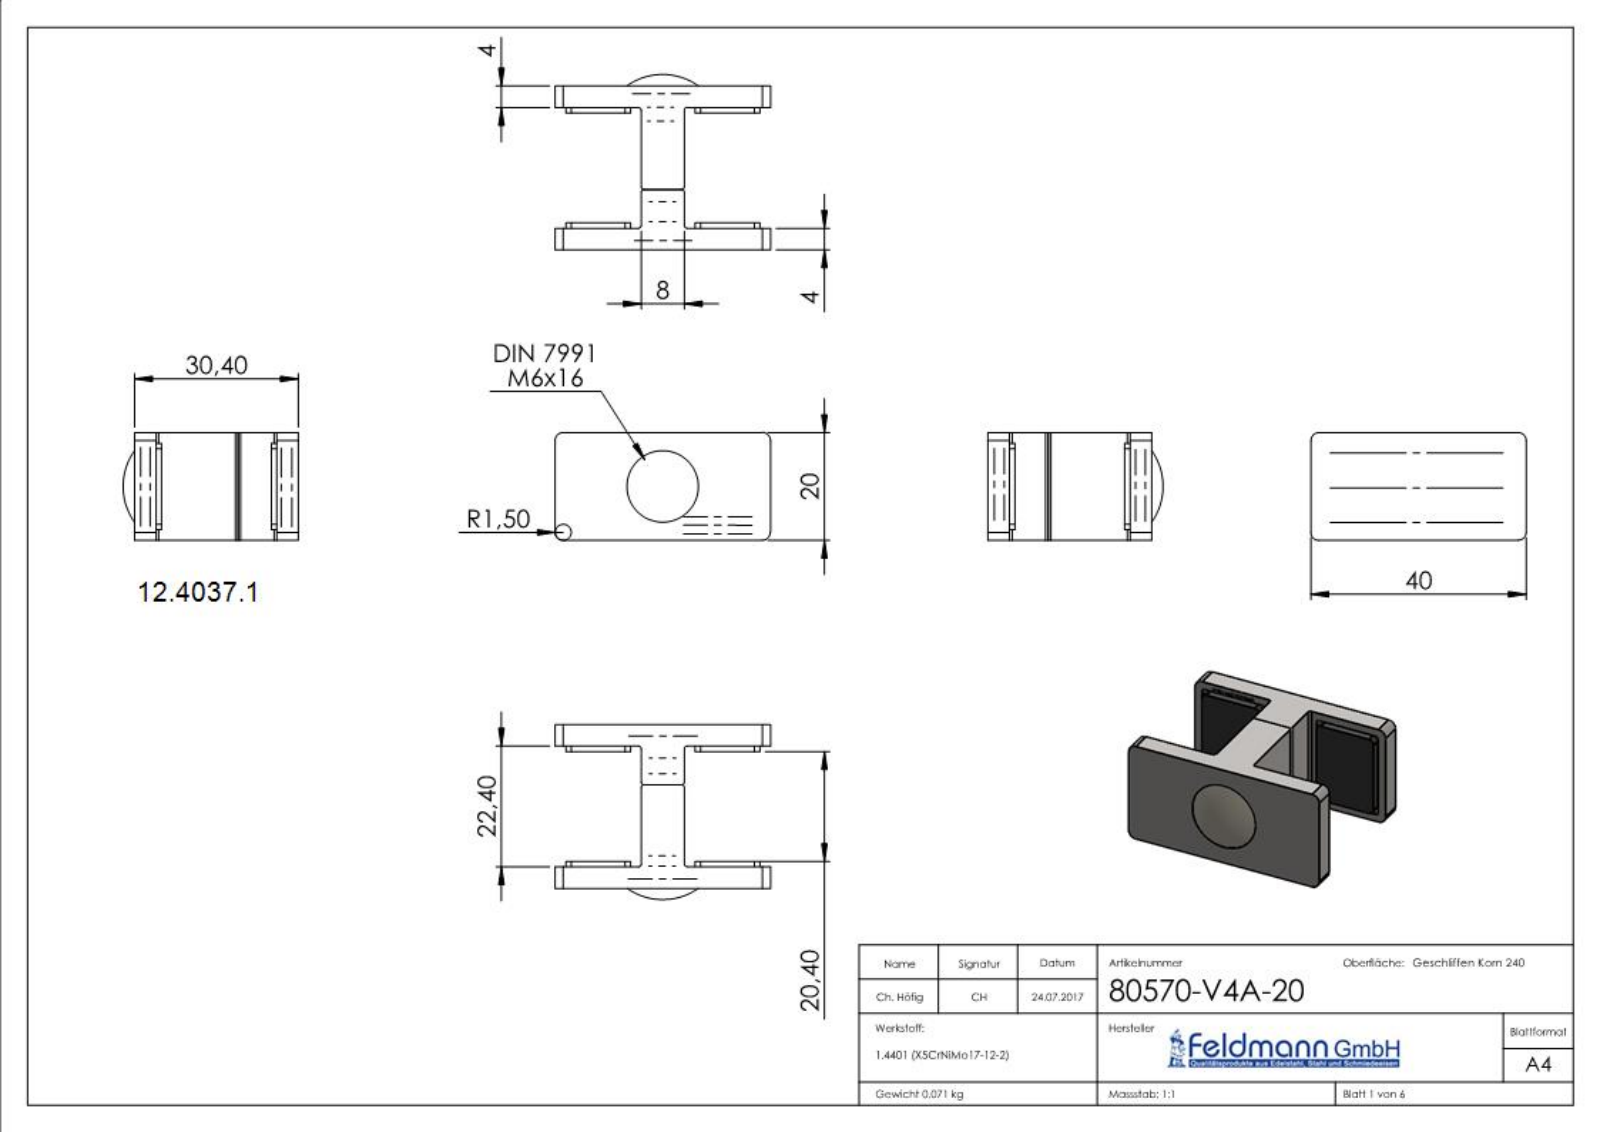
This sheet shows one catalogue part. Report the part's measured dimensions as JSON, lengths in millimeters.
{"part_name": "80570-XXX-XX Teil4_80570-XXX-XX Teil4; 80570-XXX-XX Teil4; 80570-V4A-20; 80570-XXX-XX Teil3_80570-240-XX Teil3 (+7 more)", "step_written_by": "SolidWorks 2018 (CONFIG_CONTROL_DESIGN)", "units": "millimeters", "bodies": {"solids": 8, "faces": 816, "planar": 380, "cylindrical": 203, "other": 233}, "overall_size": [40, 32.51, 20], "volume_mm3": 10149, "surface_area_mm2": 9084, "round_holes": [[2.7, 2], [1.8, 1], [5, 1], [6.5, 1], [12.5, 1]], "round_bosses_or_shafts": [[12, 1], [6, 1], [4, 1]], "partial_cylinders_radius": [[0.5, 80], [0.2, 12], [1, 8], [0.19, 4], [1.5, 4]], "face_to_face_distances": [3.5, 26.9, 1.5, 5, 30.4, 25.4, 21.9, 23.4, 2, 8], "hole_center_spacings": [6.5, 13]}
